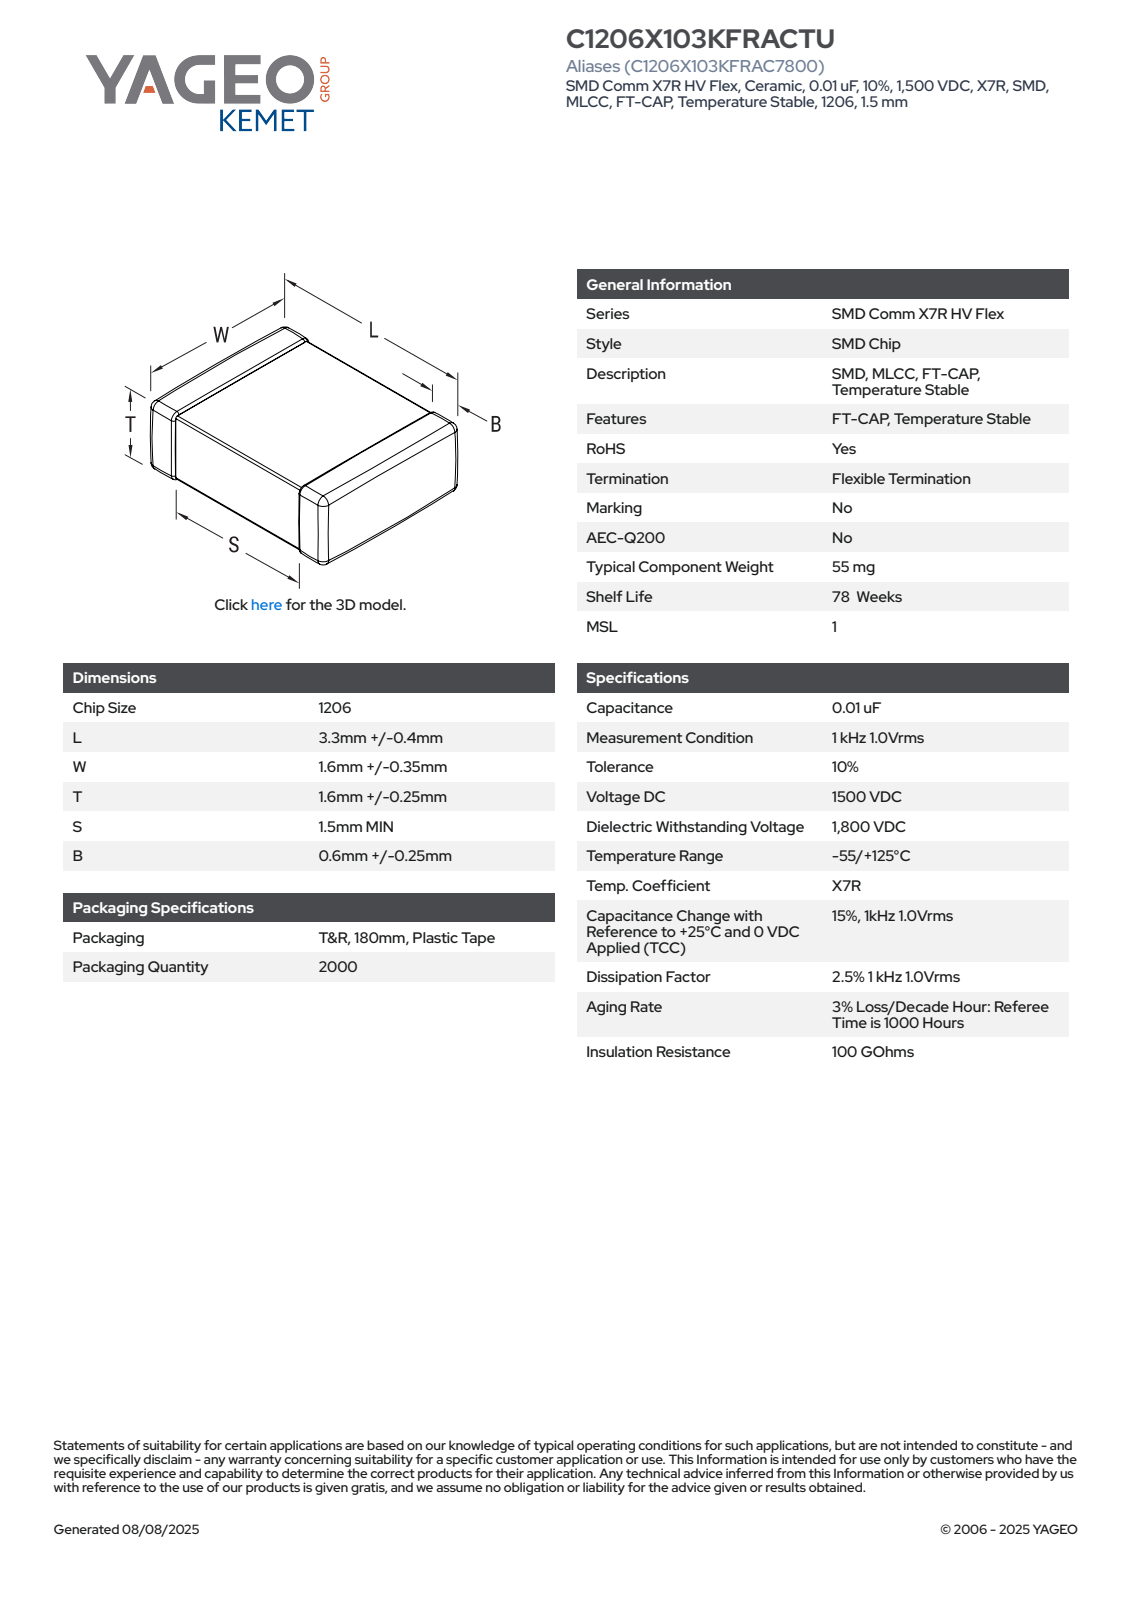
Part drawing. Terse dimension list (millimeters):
name: CCS_CCSTDNOS_1206_L3.7W1.95T1.85B0.85
written by: SolidWorks 2014 (AUTOMOTIVE_DESIGN)
unit: mm
bodies: 4 solids, 125 faces (71 planar, 38 cylindrical, 16 other)
size: 3.7 × 1.95 × 1.85
volume: 13 mm³; area: 35 mm²
face distances: 1.81, 1.91, 1.77, 1.87, 3.7, 1.85, 1.95, 0.86, 0.82, 1.05
